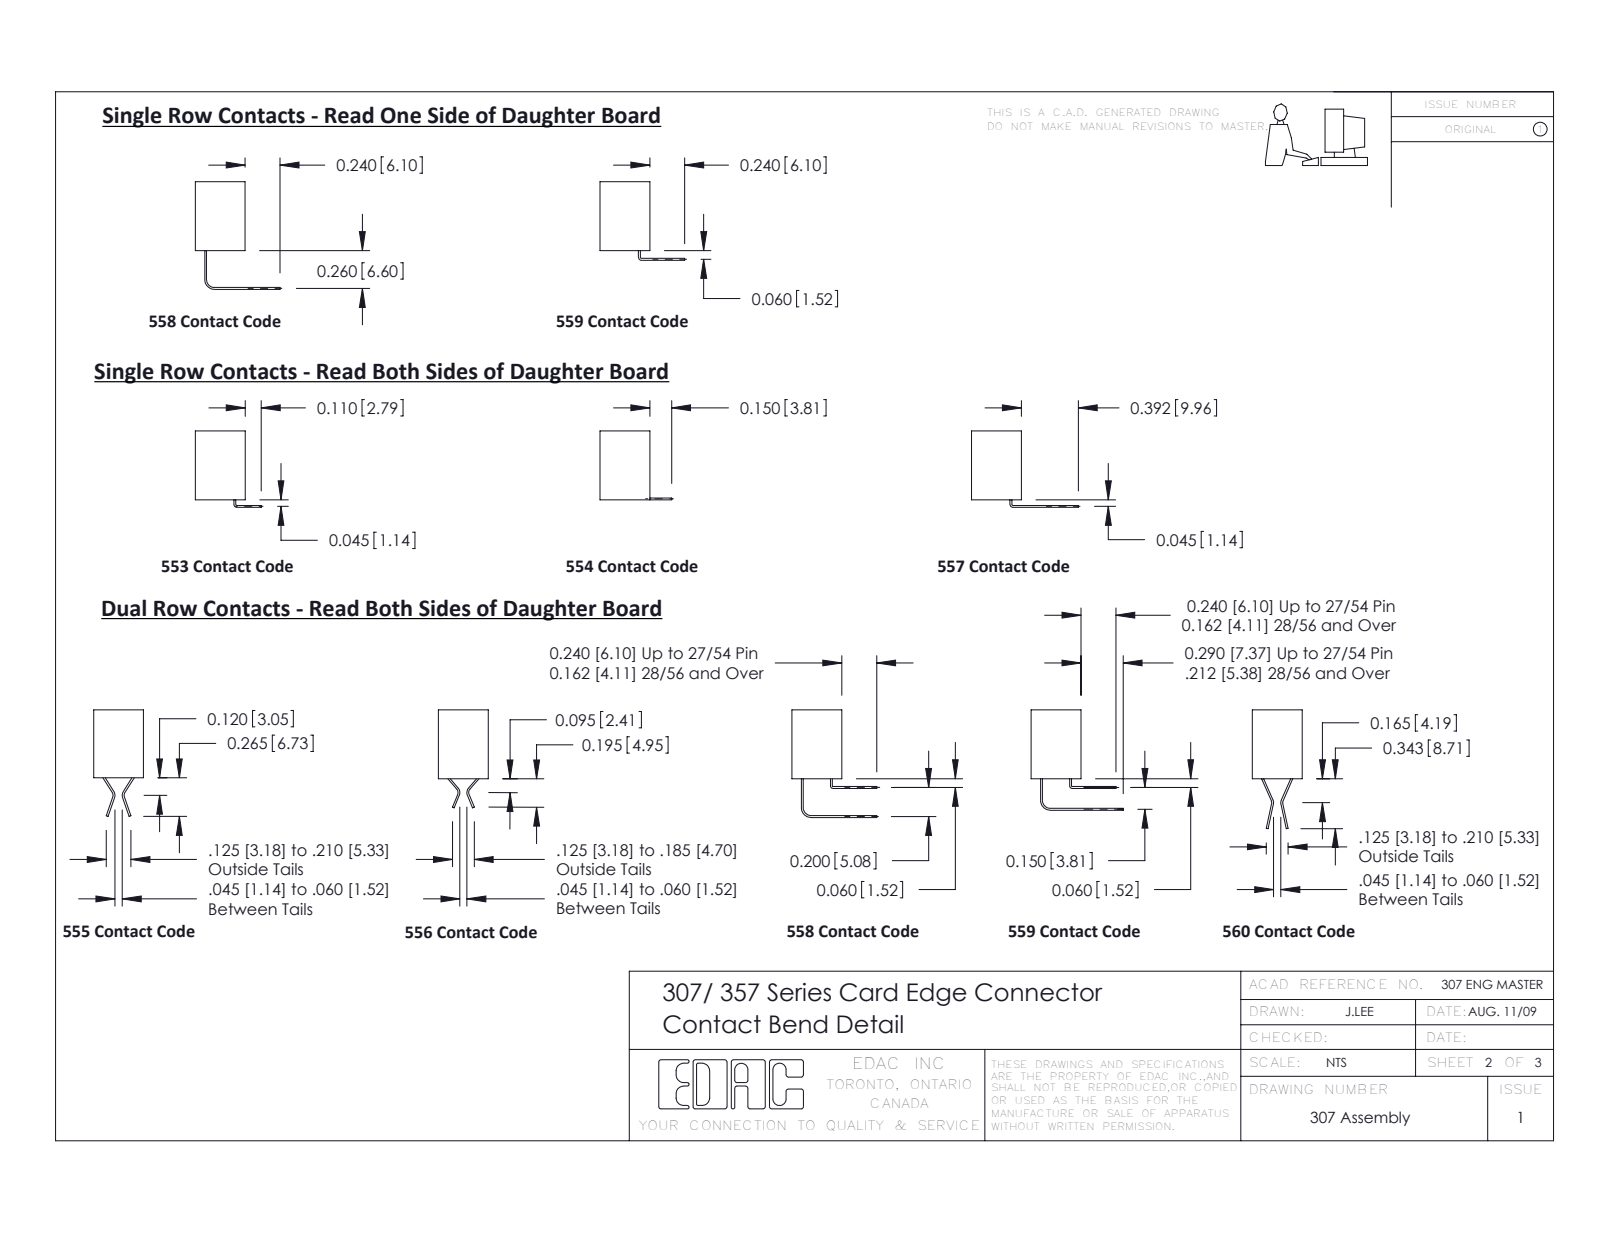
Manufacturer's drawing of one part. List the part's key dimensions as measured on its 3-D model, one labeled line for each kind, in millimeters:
Part name (STEP PRODUCT): 307-220-068; 357-031-547-168; 307-290-001_547; 307 Part_.156 Dia Mounting Holes (+1 more)
STEP written by: SolidWorks 2016 (CONFIG_CONTROL_DESIGN)
Units: millimetres
Bodies: 36 solids, 2040 faces (1305 planar, 647 cylindrical, 88 other)
Overall size (bounding box): 150.3 × 83.4 × 12.7
Volume: 19 990 mm³ · Surface area: 20 920 mm²
Round holes (diameter × count): ⌀2.3 ×2, ⌀3.2 ×2, ⌀4 ×2
Round bosses / shafts (diameter × count): ⌀3.9 ×2
Partial cylindrical surfaces — rounded edges, fillets, slot ends (radius × count): R0.5 ×161, R0.6 ×31, R0.3 ×22, R0.8 ×16, R0.2 ×6, R0.8 ×6, R0.7 ×3, R1.2 ×2
Main face-to-face distances: 10.7, 8.7, 3.6, 9.1, 2, 9.1, 12.7, 4, 3.6, 0.3
Hole centre spacings: 138
